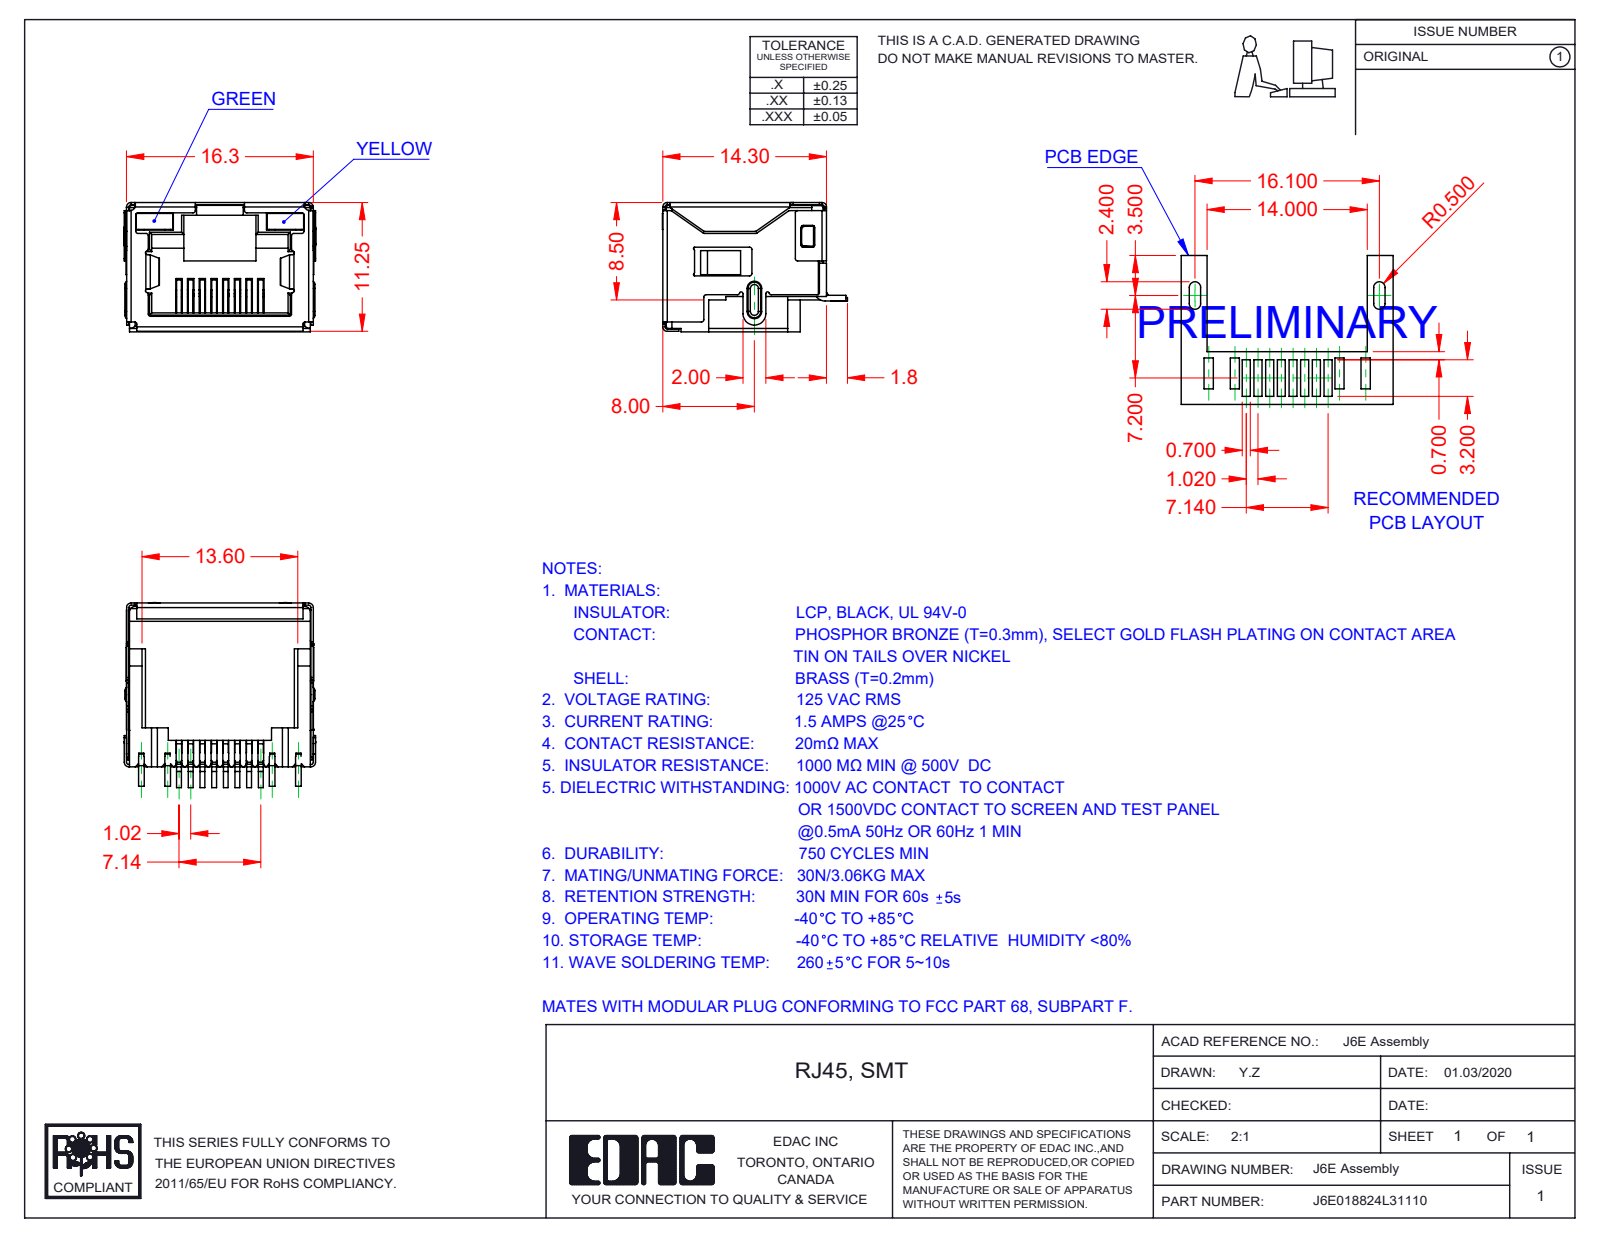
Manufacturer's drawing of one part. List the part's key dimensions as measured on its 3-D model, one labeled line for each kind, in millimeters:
Part name (STEP PRODUCT): 6E LED RH_1-Yellow; 6E LED LH_3-Green; 6E Shield_LED; 6E Insulator_LED (+2 more)
STEP written by: SolidWorks 2016 (CONFIG_CONTROL_DESIGN)
Units: millimetres
Bodies: 12 solids, 1496 faces (1099 planar, 347 cylindrical, 50 other)
Overall size (bounding box): 16.75 × 16.15 × 11.3
Volume: 1 109 mm³ · Surface area: 4 045 mm²
Partial cylindrical surfaces — rounded edges, fillets, slot ends (radius × count): R0.2 ×82, R0.25 ×17, R0.4 ×13, R0.5 ×13, R0.1 ×10, R0.15 ×7, R0.3 ×4, R1 ×3
Main face-to-face distances: 11.05, 16.05, 16.1, 15.85, 11.1, 11.3, 2.4, 0.7, 9.85, 0.49
